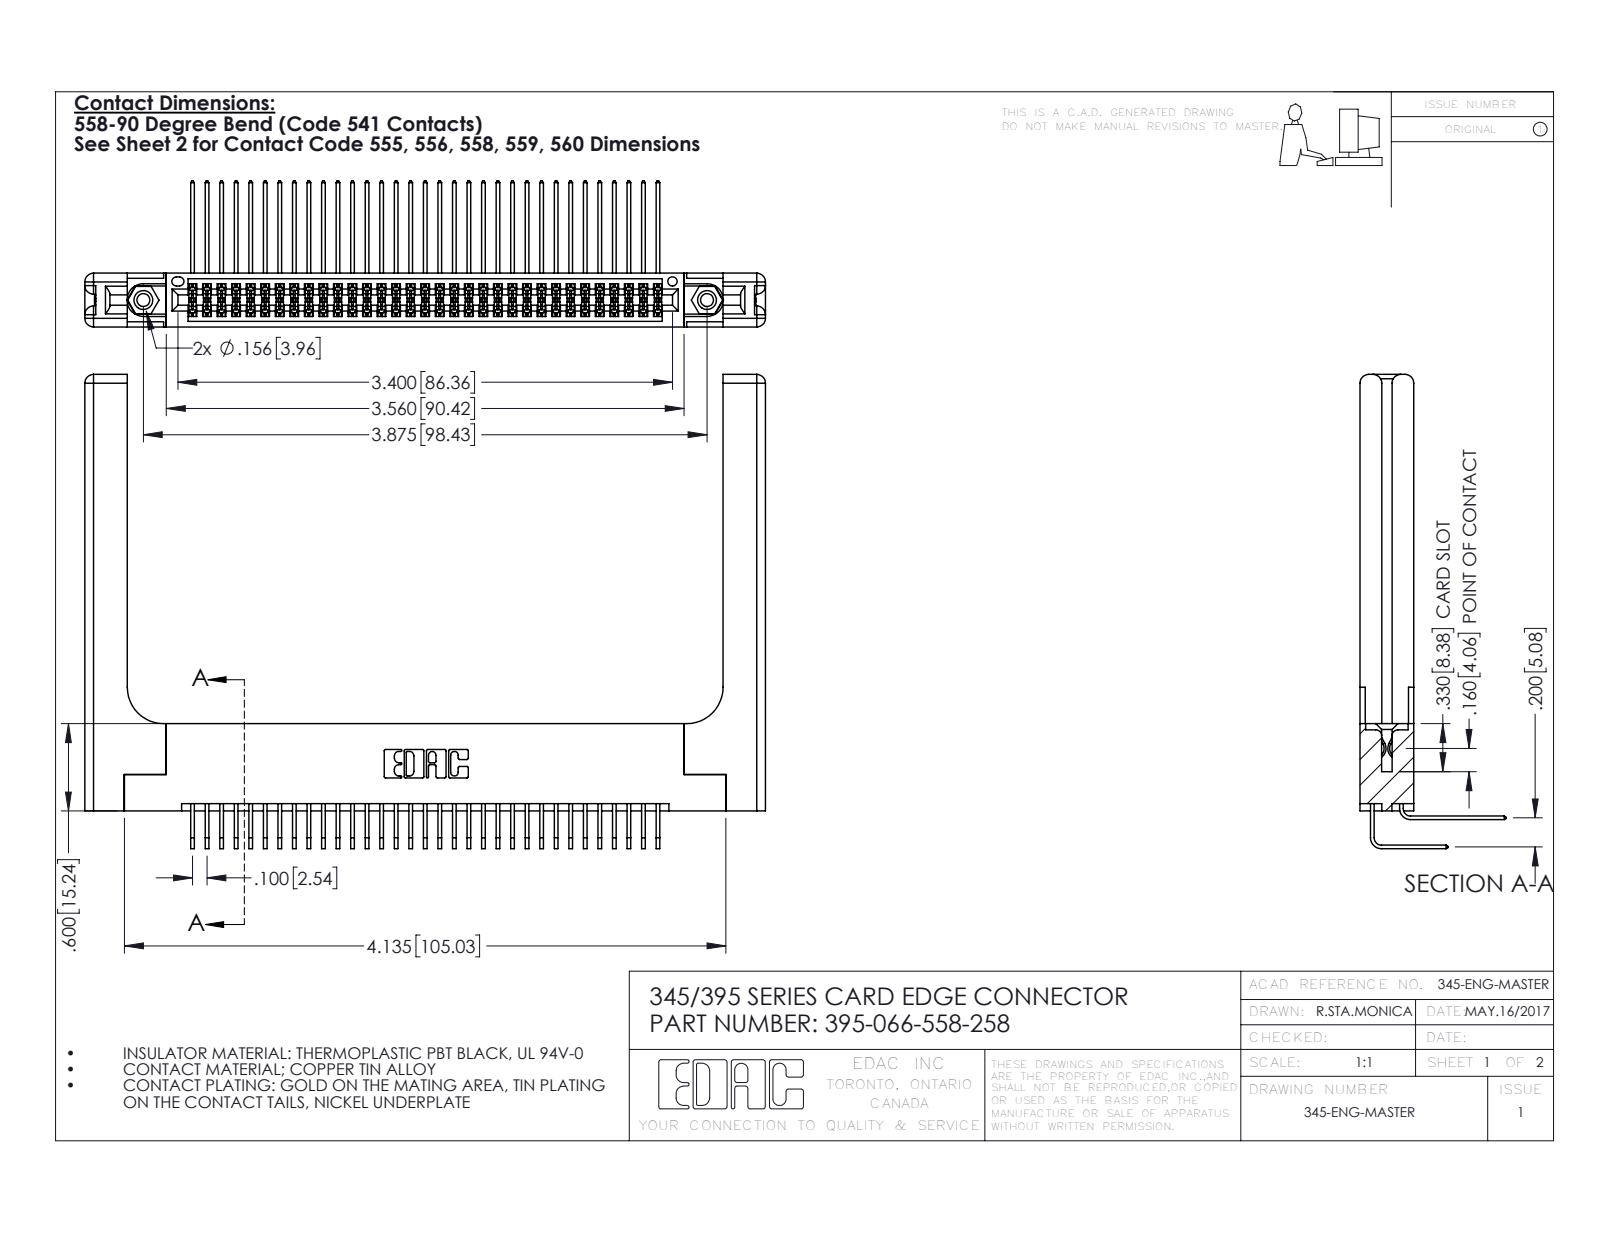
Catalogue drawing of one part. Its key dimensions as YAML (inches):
part_name: "395-066-558-258; 345-250-001_345-250-001-102; 345-292-001_558 Tail - 2; 345-220-058_345-220-058 (+2 more)"
step_written_by: "SolidWorks 2016 (CONFIG_CONTROL_DESIGN)"
units: inches
bodies: {solids: 71, faces: 3814, planar: 2538, cylindrical: 1216, other: 60}
overall_size: [4.679, 3.259, 1.005]
volume: 1.24
surface_area: 37.48
round_holes:
  - {diameter: 0.089, count: 2}
  - {diameter: 0.125, count: 2}
  - {diameter: 0.156, count: 2}
  - {diameter: 0.064, count: 1}
round_bosses_or_shafts:
  - {diameter: 0.155, count: 2}
partial_cylinders:
  - {radius: 0.006, count: 100}
  - {radius: 0.01, count: 22}
  - {radius: 0.06, count: 16}
  - {radius: 0.007, count: 6}
  - {radius: 0.031, count: 6}
  - {radius: 0.026, count: 3}
  - {radius: 0.014, count: 2}
  - {radius: 0.019, count: 2}
face_to_face_distances: [0.072, 0.37, 0.298, 0.2, 0.098, 0.272, 0.025, 0.225, 0.148, 0.15]
hole_center_spacings: [0.27, 3.64, 3.875]
